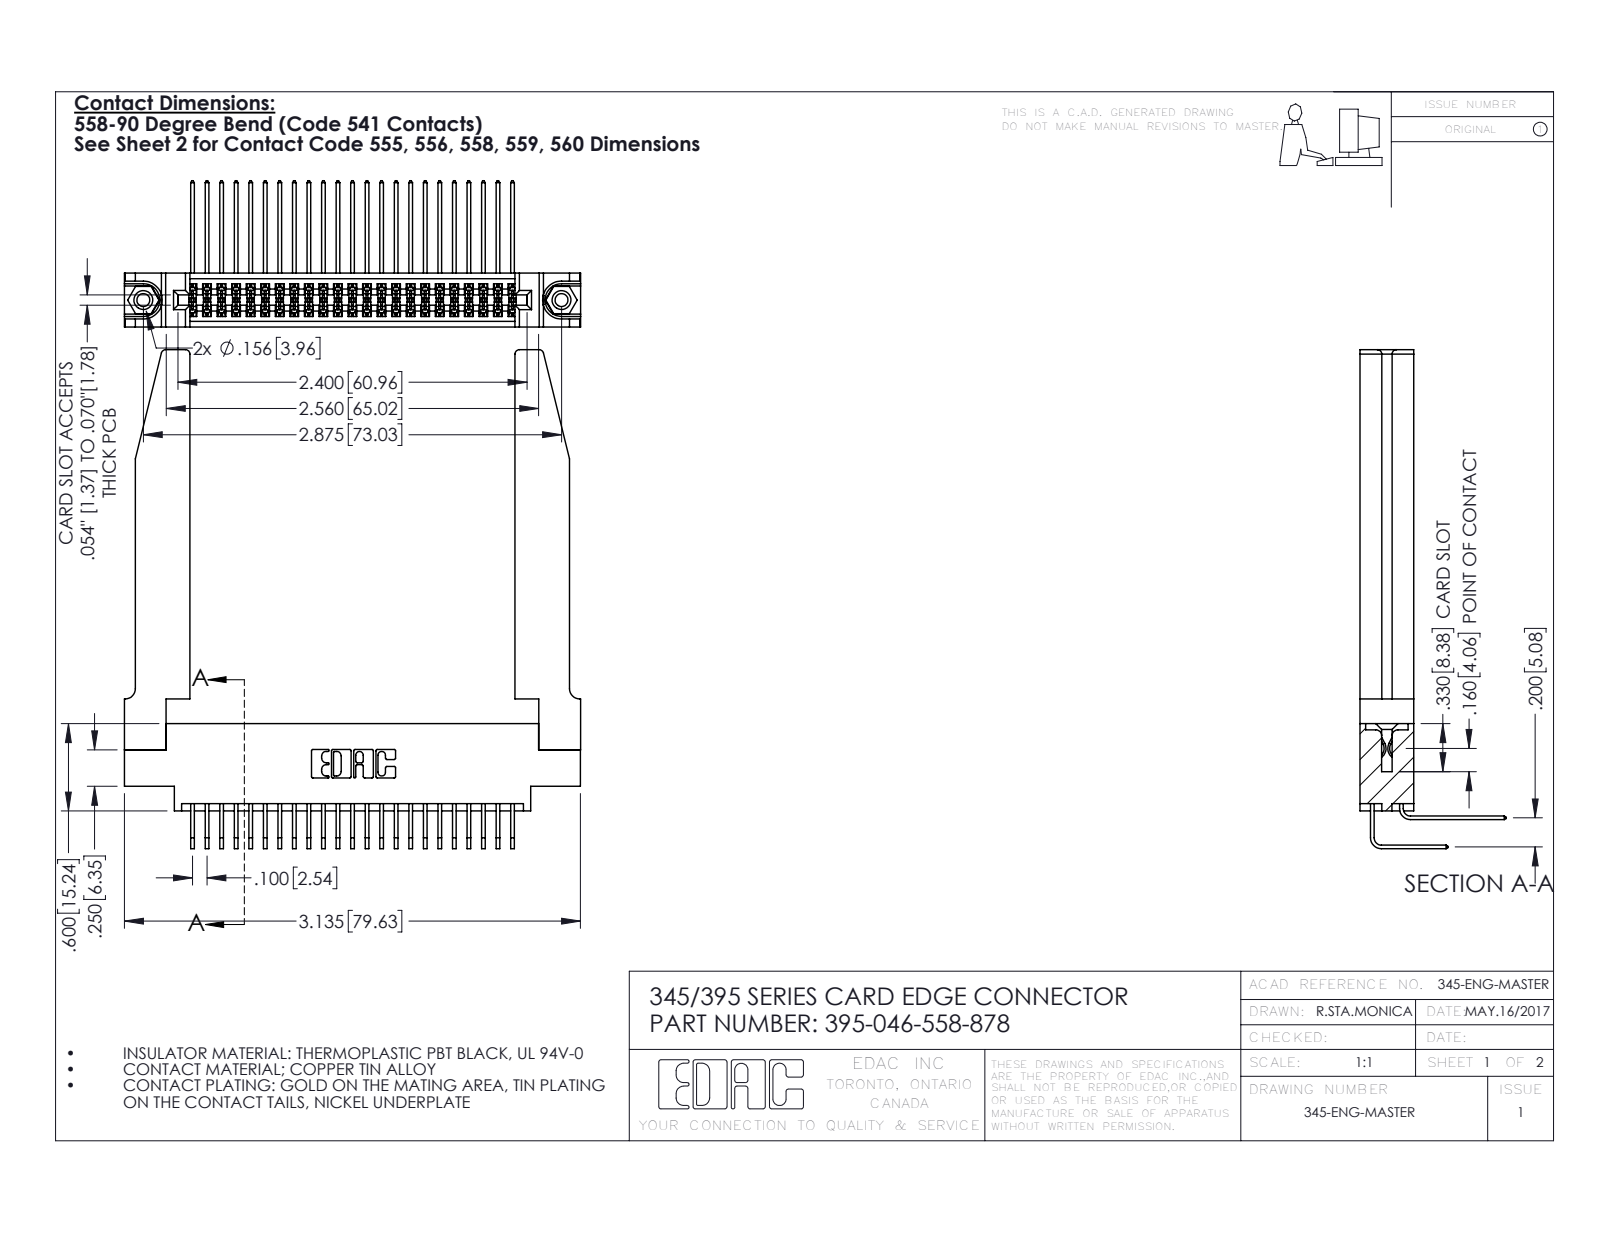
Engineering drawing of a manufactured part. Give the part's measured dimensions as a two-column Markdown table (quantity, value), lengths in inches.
| quantity | value |
| --- | --- |
| part name | 345-292-001_558 559 Tail - 1; 345-220-078_345-220-078; 345-250-001_345-250-001-102; 345-292-001_558 Tail - 2 (+2 more) |
| STEP written by | SolidWorks 2016 (CONFIG_CONTROL_DESIGN) |
| units | inches |
| bodies | 51 solids, 2756 faces (1836 planar, 868 cylindrical, 52 other) |
| overall size | 3.429 × 3.136 × 1.005 |
| volume | 0.945 in³ |
| surface area | 29.86 in² |
| round holes (diameter × count) | 0.089 × 2, 0.125 × 2, 0.156 × 2, 0.064 × 1 |
| round bosses / shafts (diameter × count) | 0.155 × 2 |
| partial cylindrical surfaces (radius × count) | 0.006 × 70, 0.01 × 22, 0.03 × 8, 0.007 × 6, 0.031 × 6, 0.026 × 3, 0.014 × 2, 0.019 × 2 |
| main face-to-face distances | 0.37, 0.072, 0.298, 0.2, 0.098, 0.272, 0.025, 0.225, 0.148, 0.15 |
| hole center spacings | 0.27, 2.641, 2.875 |
